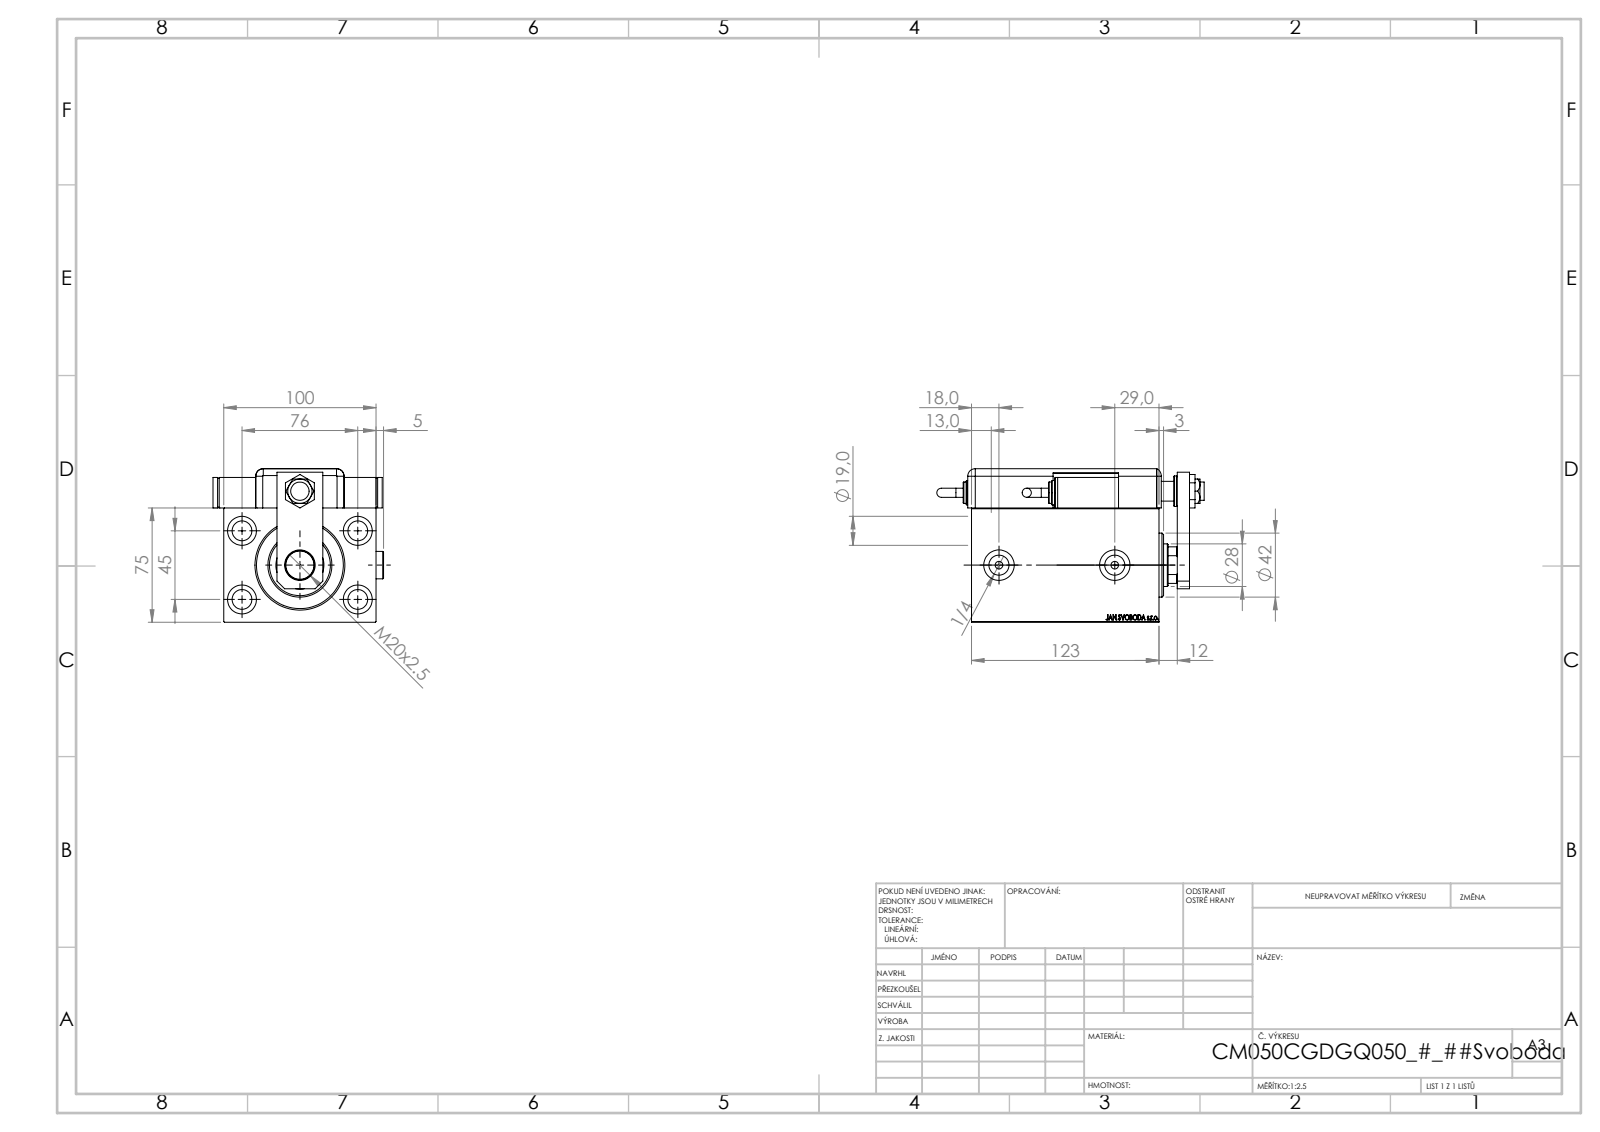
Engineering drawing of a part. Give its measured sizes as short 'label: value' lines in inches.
name: V450CM_C_VCP; ZARAZKA_Q; SWITCH Q; V450CM_VC_B (+7 more)
written by: SolidWorks 2019 (CONFIG_CONTROL_DESIGN)
unit: in
bodies: 15 solids, 1303 faces (649 planar, 133 cylindrical, 521 other)
size: 6.908 × 4.406 × 3.969
volume: 56.32 in³; area: 291.3 in²
holes: 5× ⌀0.512, 4× ⌀0.748, 3× ⌀0.787, 2× ⌀0.157, 2× ⌀0.197, 2× ⌀0.315, 2× ⌀0.518, 1× ⌀0.472, 1× ⌀0.551, 1× ⌀0.728, 1× ⌀1.102, 1× ⌀1.24
bosses: 3× ⌀0.787, 2× ⌀0.709, 2× ⌀0.63, 2× ⌀0.551, 2× ⌀0.236, 1× ⌀1.654
rounds: 9× R0.197, 1× R0.394, 1× R0.531
face distances: 2.953, 0.118, 3.937, 1.016, 3.969, 0.551, 0.787, 0.531, 4.843, 4.291
hole spacings: 1.739, 2.992, 1.772, 1.813, 3.17, 3.477, 0.787, 1.909
